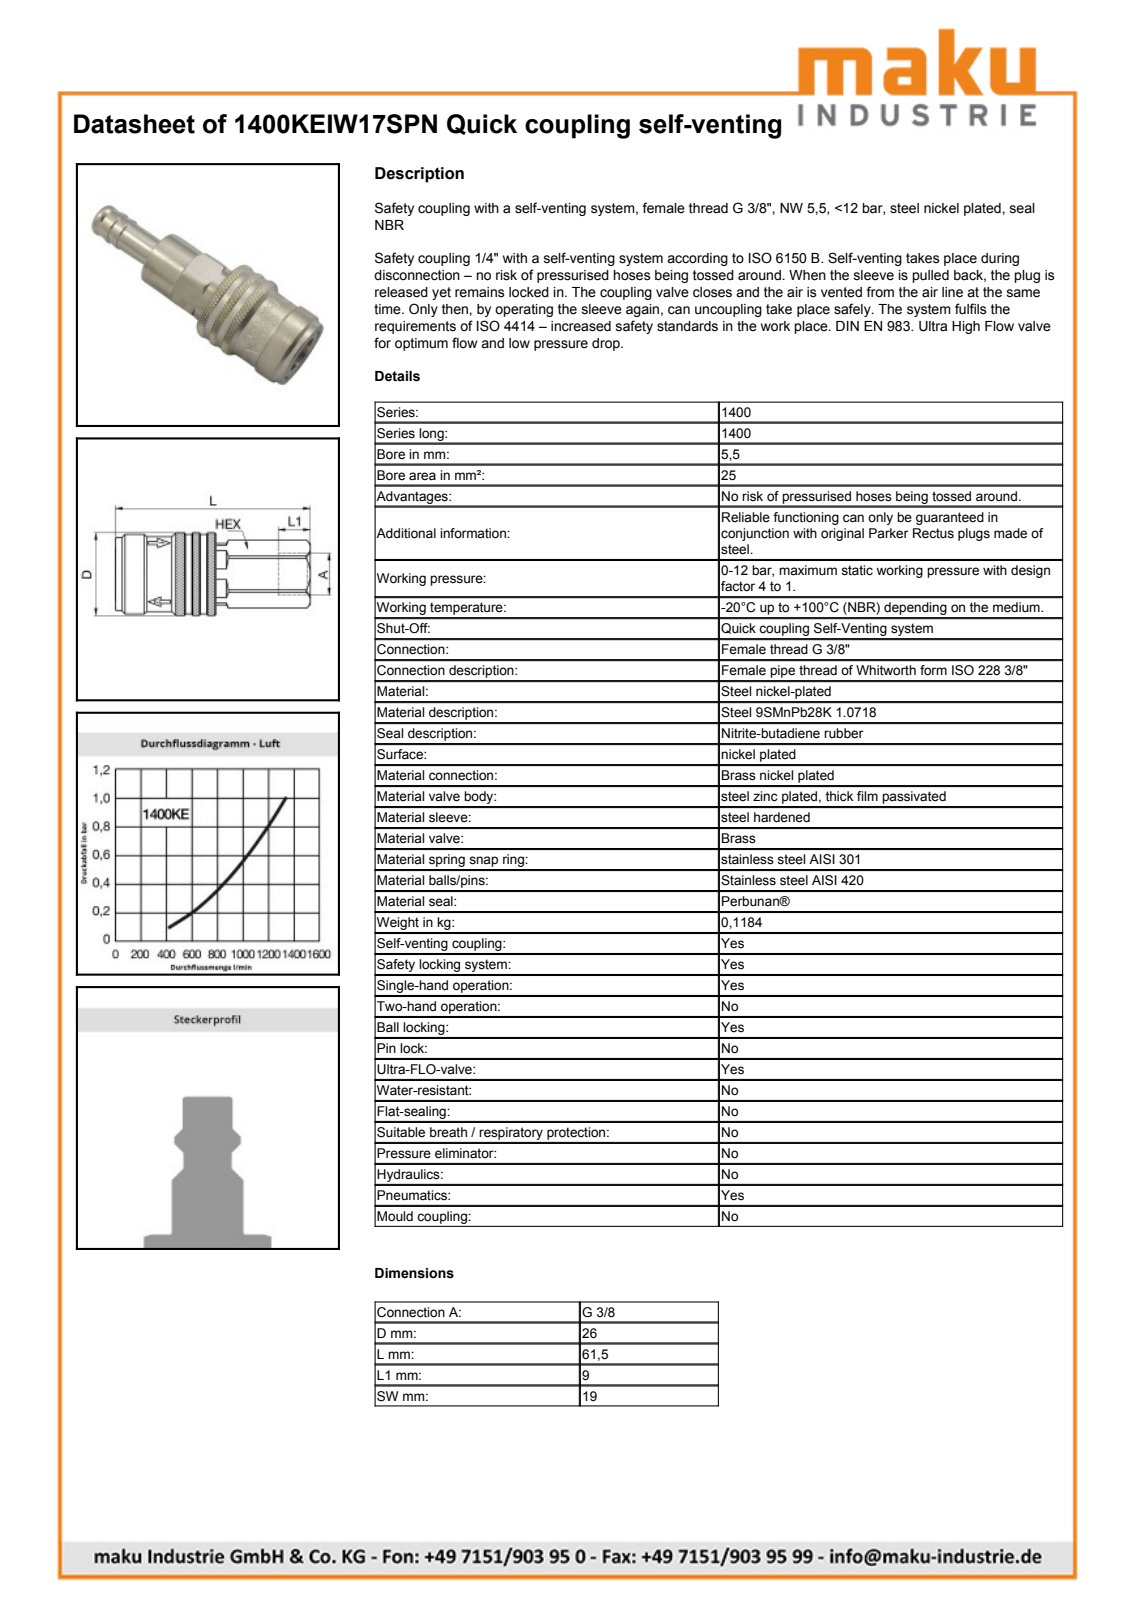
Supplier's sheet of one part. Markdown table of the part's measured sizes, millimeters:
| quantity | value |
| --- | --- |
| part name | 1400KEIW17SPN |
| STEP written by | Autodesk Inventor 2014 (AUTOMOTIVE_DESIGN) |
| units | millimeters |
| bodies | 1 solid, 674 faces (297 planar, 76 cylindrical, 301 other) |
| overall size | 61.5 × 27 × 27 |
| volume | 23 230 mm³ |
| surface area | 6 098 mm² |
| round holes (diameter × count) | 15.25 × 1 |
| round bosses / shafts (diameter × count) | 27 × 1, 26 × 1, 25 × 1, 23.5 × 1, 23 × 1 |
| partial cylindrical surfaces (radius × count) | 9.65 × 1, 10.7 × 1, 11.55 × 1 |
| main face-to-face distances | 19, 31.8, 20.69, 52.49, 52.19, 31.5, 9.01, 29.7, 61.2, 61.5 |
